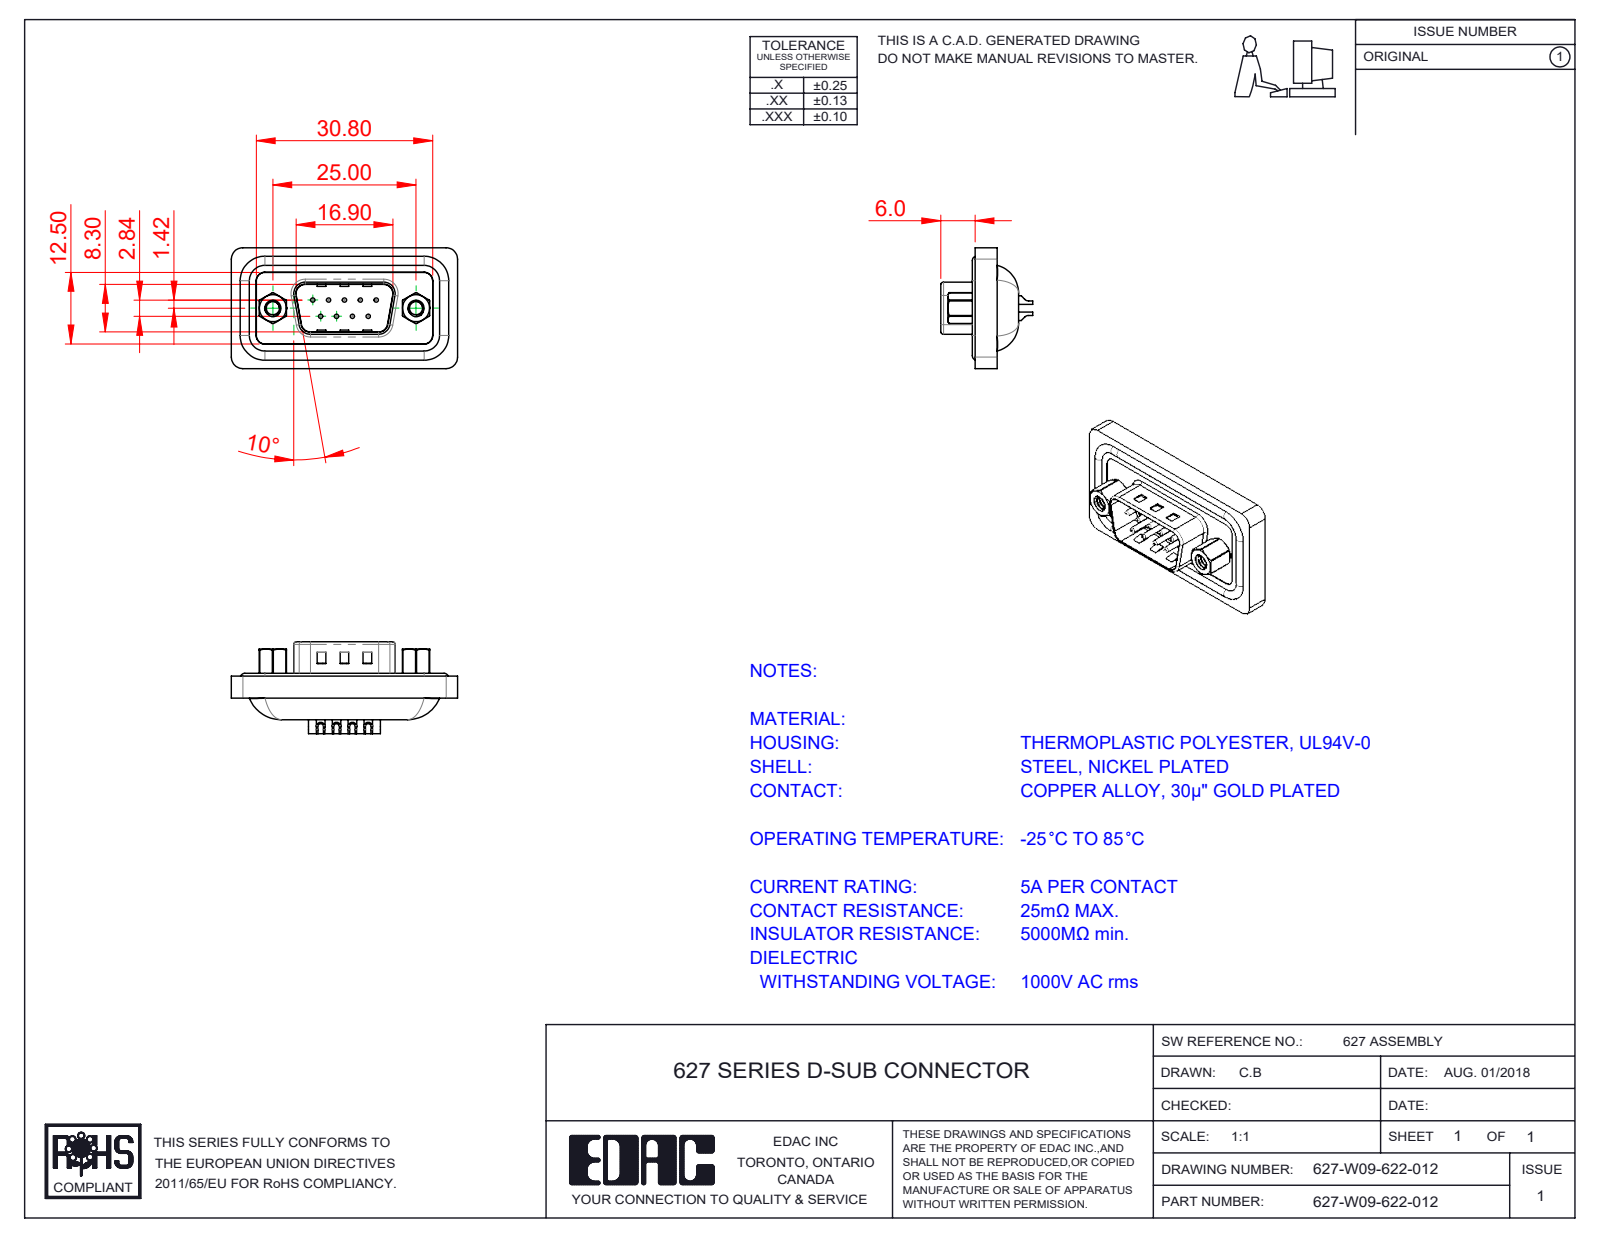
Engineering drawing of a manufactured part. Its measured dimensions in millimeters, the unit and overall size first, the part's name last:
Units: millimetres
Overall size (bounding box): 39.5 × 21.1 × 16.05
Round holes (diameter × count): ⌀0.75 ×9, ⌀1 ×9, ⌀1.5 ×9, ⌀1.6 ×9, ⌀2 ×9, ⌀2.26 ×2, ⌀2.29 ×2, ⌀4 ×2, ⌀4.8 ×2, ⌀5 ×2
Round bosses / shafts (diameter × count): ⌀1.6 ×4, ⌀4.9 ×2, ⌀2.79 ×2
Partial cylindrical surfaces — rounded edges, fillets, slot ends (radius × count): R2 ×16, R1.5 ×14, R0.5 ×8, R2.7 ×6, R0.9 ×4, R1.6 ×4, R4.3 ×4, R0.4 ×2
Main face-to-face distances: 0.4, 0.75, 1.1, 2.75, 3.75, 0.5, 1, 3.5, 1.85, 1.6
Hole centre spacings: 3.16, 2.77, 5.54, 5.03, 5.04, 8.31, 7.1, 7.48
Volume: 4 666 mm³ · Surface area: 6 636 mm²
Bodies: 17 solids, 799 faces (222 planar, 374 cylindrical, 203 other)
Part name (STEP PRODUCT): 627W 4-40 Threaded Rivet; 627W Housing_09 Contacts; 627W 4-40 Hex Standoff; 627W Waterproof Housing_09 Contacts (+4 more)
STEP written by: SolidWorks 2020 (CONFIG_CONTROL_DESIGN)
